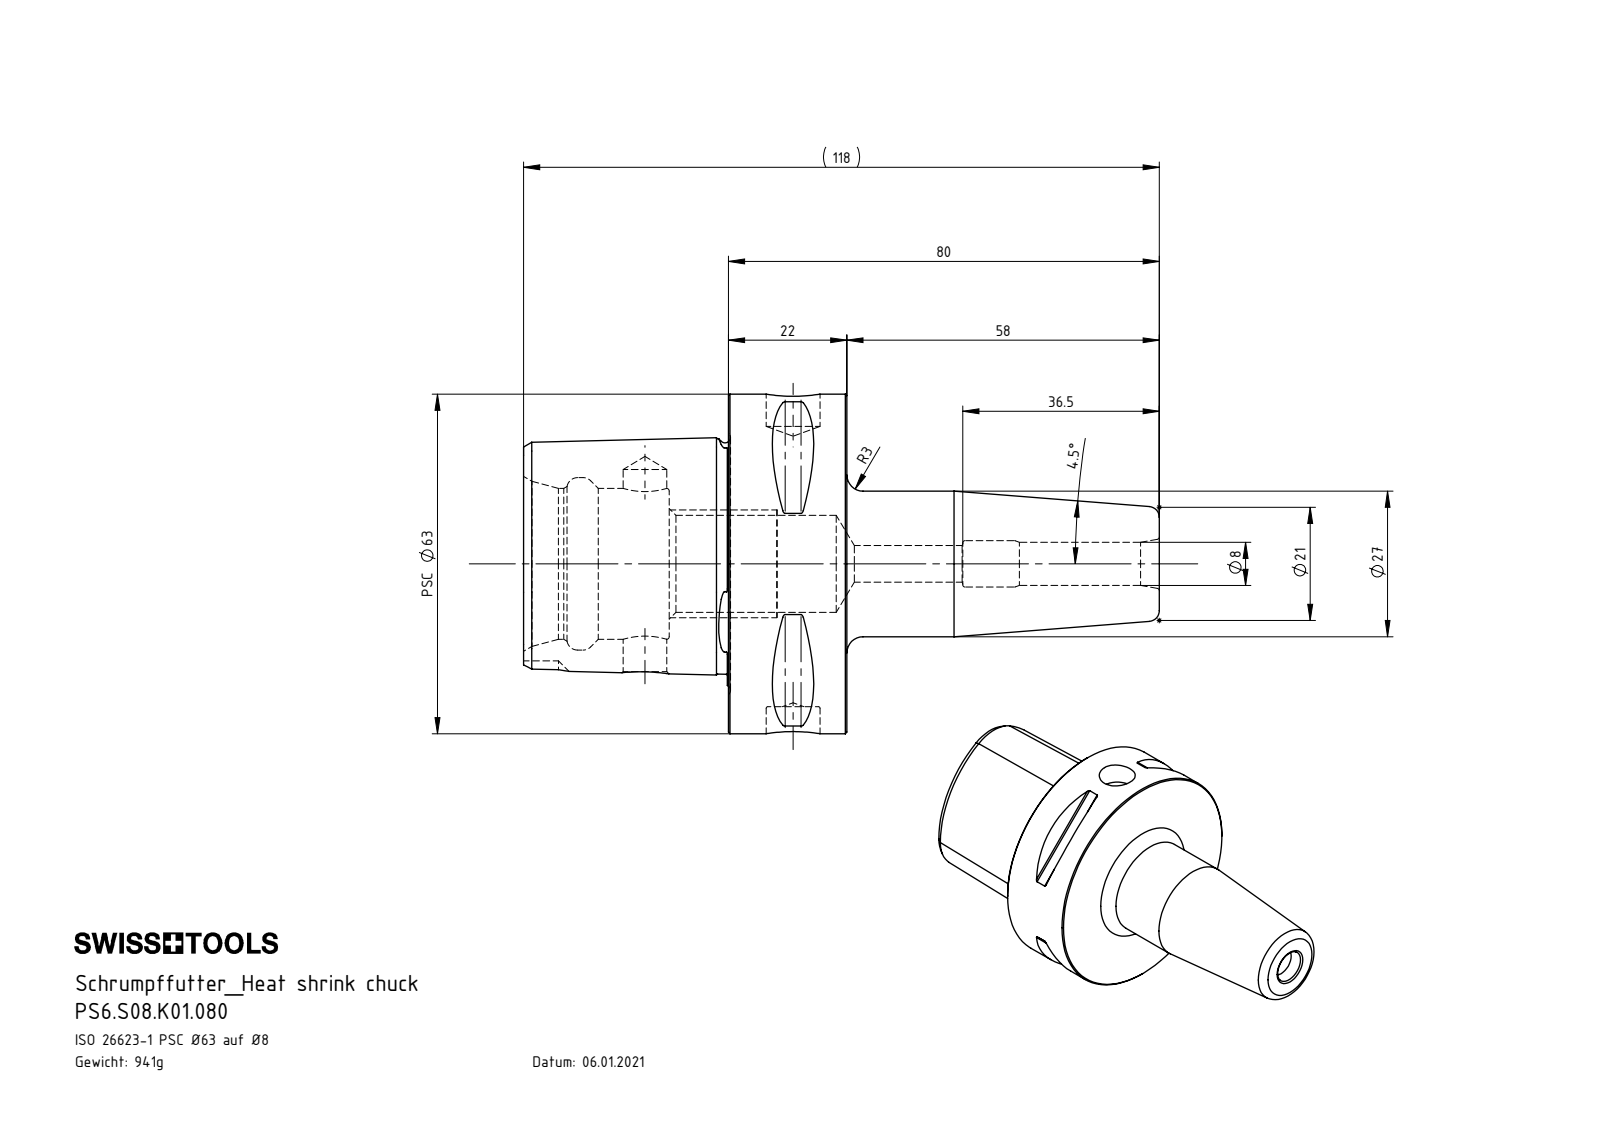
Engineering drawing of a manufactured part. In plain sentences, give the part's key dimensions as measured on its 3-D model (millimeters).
The part is named "PS6.S08.K01.080". Its 3-D file was written by "SolidWorks 2022 (AUTOMOTIVE_DESIGN)". It is 1 solid with 152 faces: 22 planar, 35 cylindrical and 95 other. Overall it measures 118 by 63 by 63 millimeters. Its volume is 119 873 cubic millimeters and its surface area 25 998 square millimeters. Round holes: 1 of diameter 6.8, 1 of diameter 8, 1 of diameter 8.1, 1 of diameter 8.6, 1 of diameter 10, 1 of diameter 18, 1 of diameter 28, 1 of diameter 32. Round bosses or shafts: 1 of diameter 63, 1 of diameter 27. Partial cylindrical surfaces (rounded edges, fillets, slot ends): 8 of radius 0.5, 1 of radius 6. The main face-to-face distances are 22, 38, 60, 24.88, 27, 11, 33, 55.8, 118, 91. The hole center spacings are 27.5.
